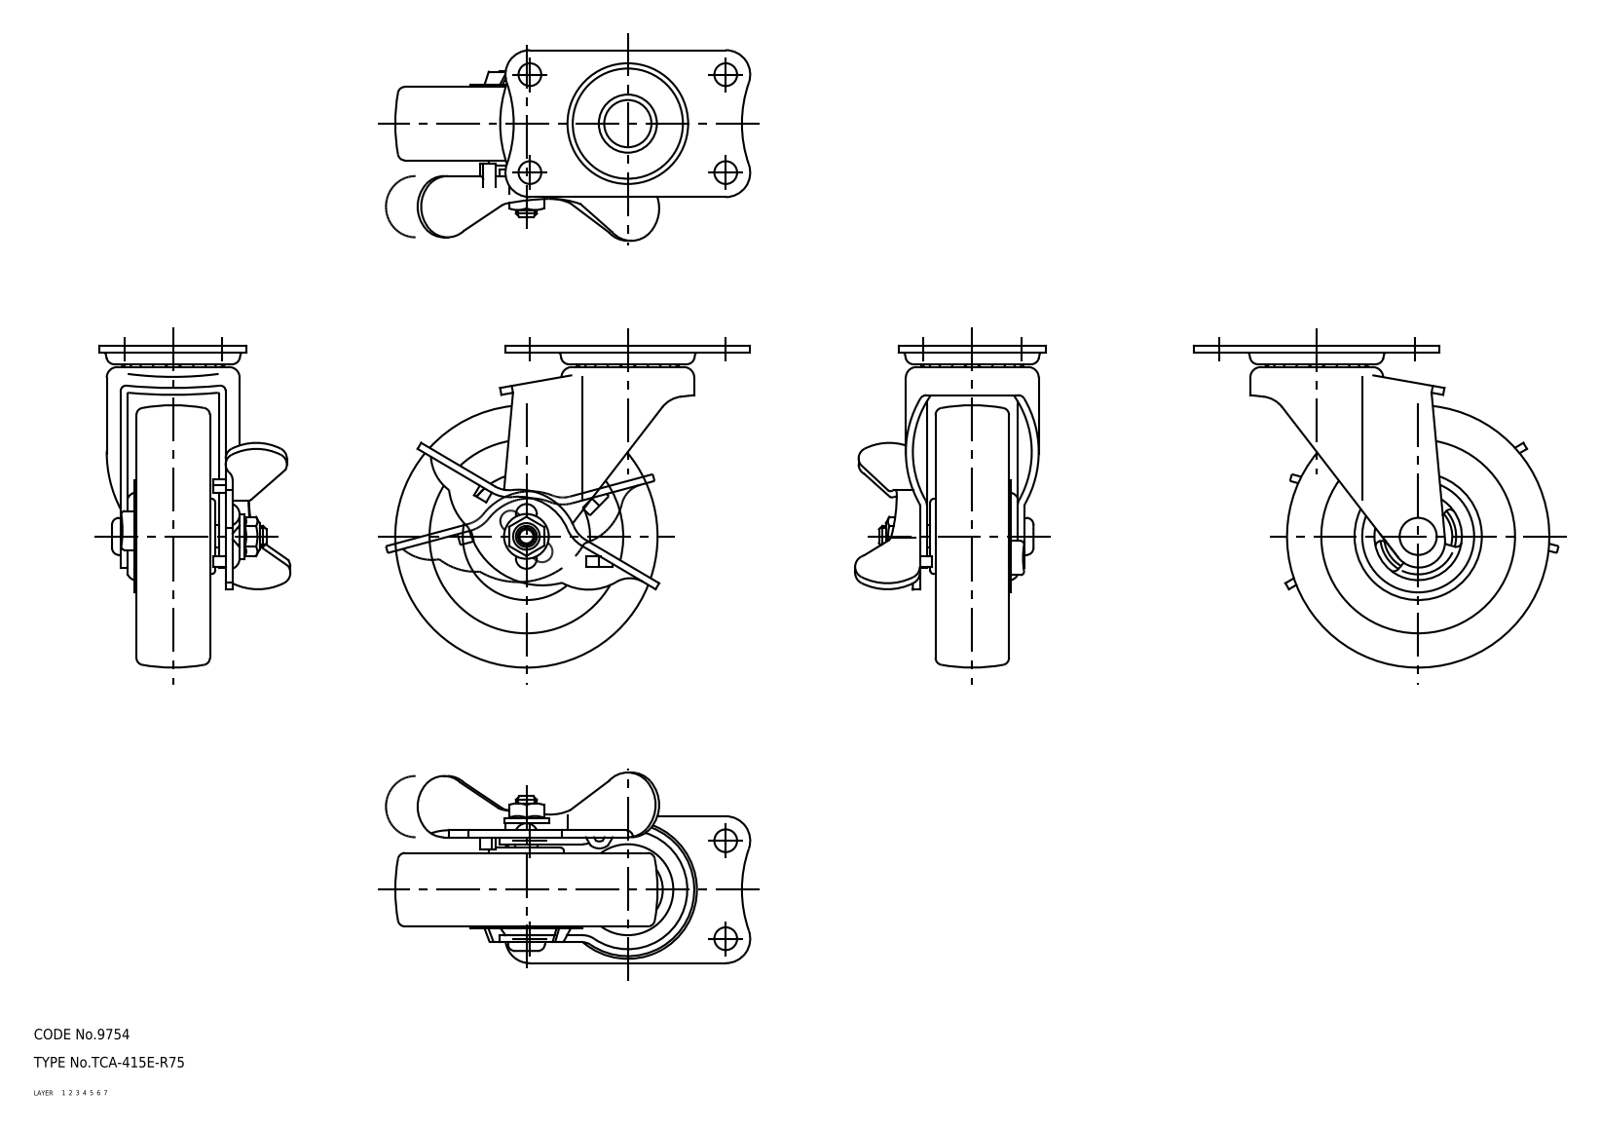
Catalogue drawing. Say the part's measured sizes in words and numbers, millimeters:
The part is named "wheel; mounting plate; main shaft; lever (+2 more)". Its 3-D file was written by "CADfix (AUTOMOTIVE_DESIGN)". It is 6 solids with 332 faces: 0 planar, 0 cylindrical and 332 other. Overall it measures 101.5 by 92 by 54.45 millimeters. Its volume is 115 428 cubic millimeters and its surface area 40 225 square millimeters.
